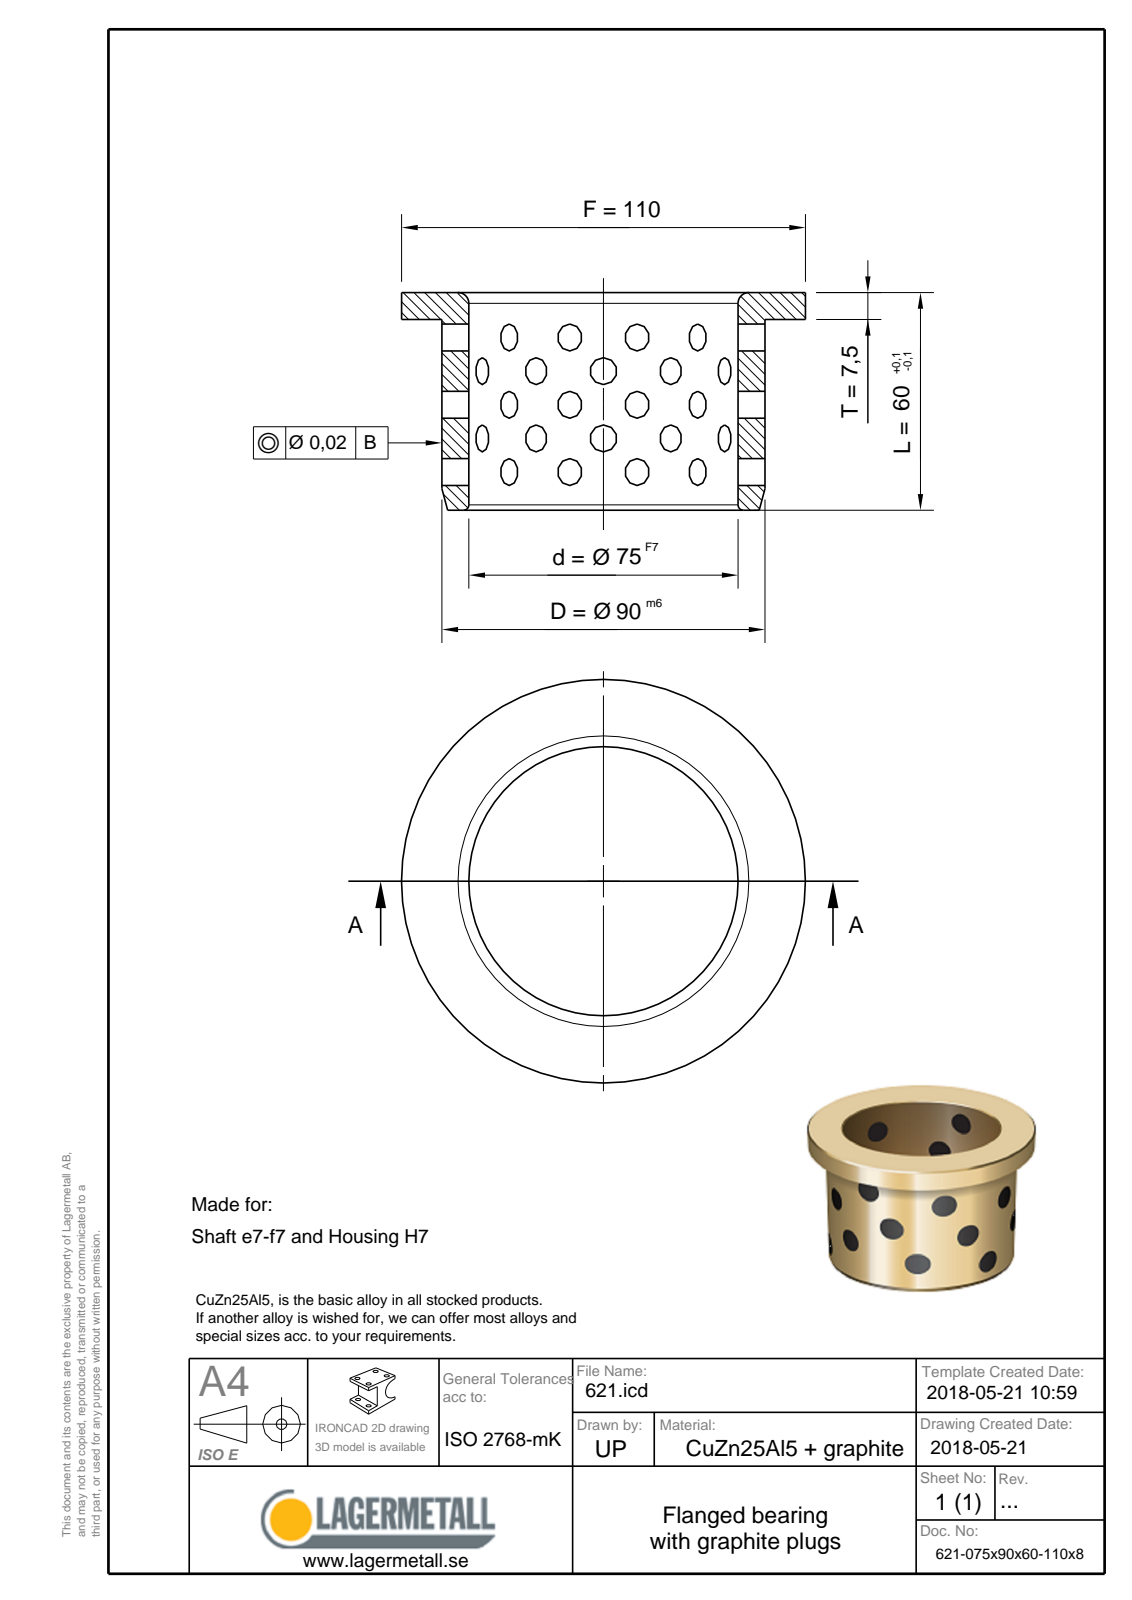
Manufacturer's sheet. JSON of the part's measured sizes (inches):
{"part_name": "621-075x90x60-110x8", "step_written_by": "Spatial InterOp 3D (CONFIG_CONTROL_DESIGN)", "units": "inches", "bodies": {"solids": 1, "faces": 9, "planar": 3, "cylindrical": 3, "other": 3}, "overall_size": [4.331, 4.331, 2.362], "volume_in3": 8.499, "surface_area_in2": 63.53, "round_holes": [[2.953, 1]], "round_bosses_or_shafts": [[4.331, 1], [3.543, 1]], "face_to_face_distances": [0.295, 2.067, 2.362]}
